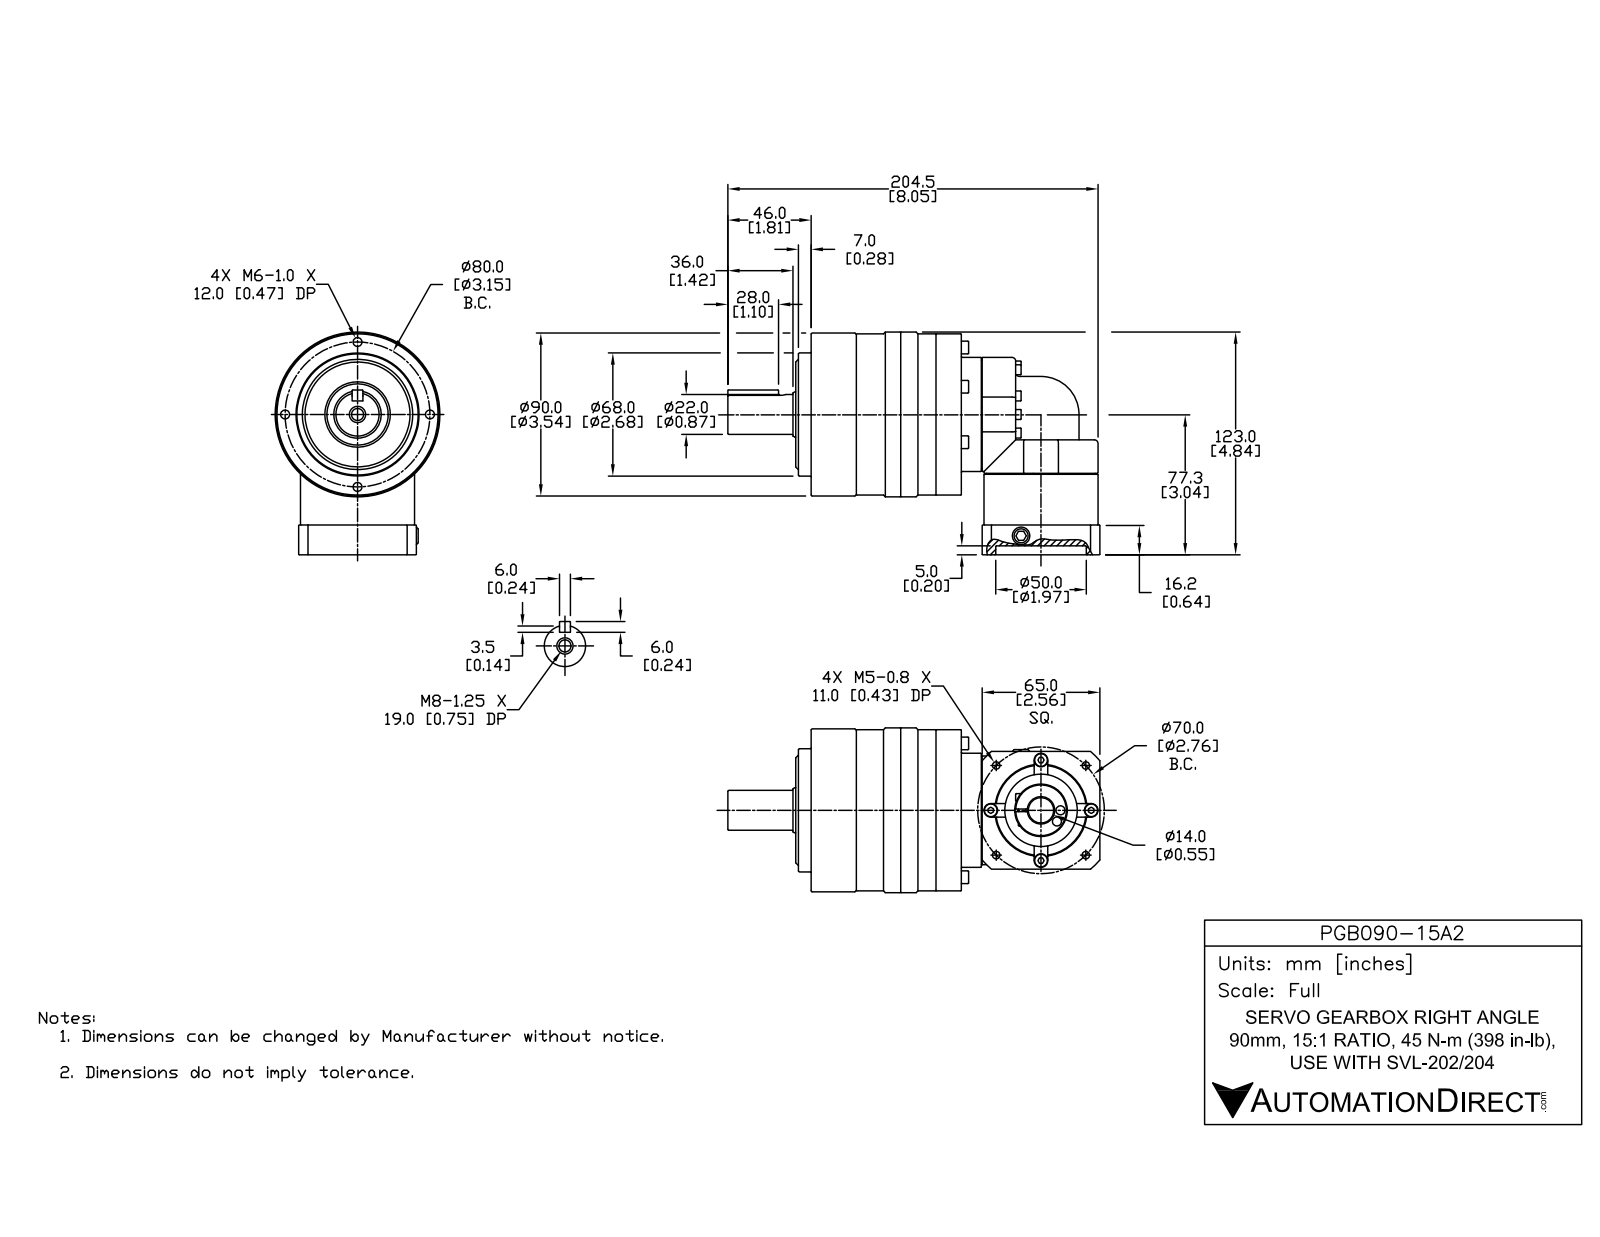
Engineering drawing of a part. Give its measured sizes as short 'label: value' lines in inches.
name: PGB090-15A2
written by: SolidWorks 2014 (AUTOMOTIVE_DESIGN)
unit: in
bodies: 1 solid, 642 faces (271 planar, 165 cylindrical, 206 other)
size: 8.091 × 4.843 × 3.583
volume: 53.54 in³; area: 120.6 in²
holes: 7× ⌀0.177, 4× ⌀0.163, 4× ⌀0.194, 4× ⌀0.295, 2× ⌀0.197, 1× ⌀0.262, 1× ⌀0.315, 1× ⌀0.551, 1× ⌀1.142, 1× ⌀1.575, 1× ⌀1.969
bosses: 11× ⌀0.276, 9× ⌀0.217, 7× ⌀0.157, 2× ⌀2.48, 2× ⌀2.362, 1× ⌀3.583, 1× ⌀3.543, 1× ⌀3.504
rounds: 6× R0.079, 2× R0.827, 1× R0.064, 1× R0.118, 1× R0.157, 1× R1.673
face distances: 0.453, 3.268, 0.335, 3.602, 2.559, 0.65, 0.098, 2.461, 0.059, 3.72
hole spacings: 0.981, 2.285, 0.615, 1.575, 1.75, 2.619, 3.089, 1.206
